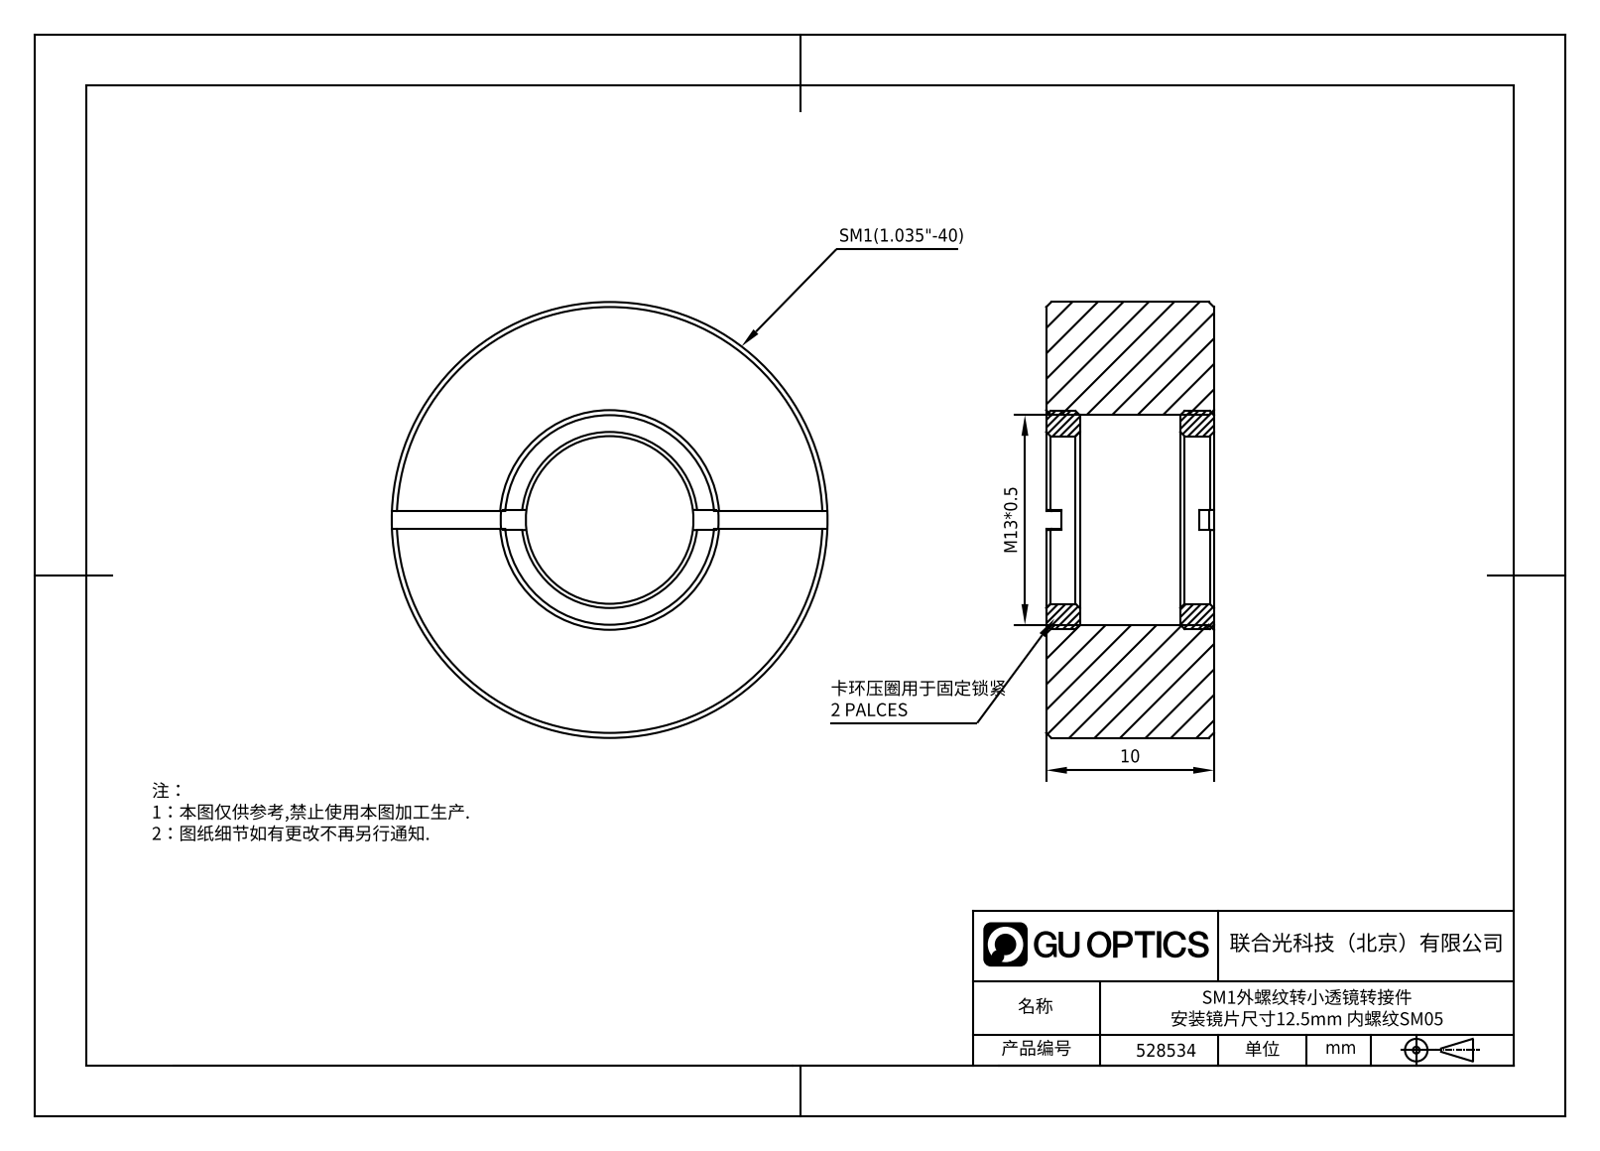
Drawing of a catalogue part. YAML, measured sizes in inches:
part_name: "528534"
step_written_by: "SolidWorks 2020 (CONFIG_CONTROL_DESIGN)"
units: inches
bodies: {solids: 3, faces: 51, planar: 27, cylindrical: 6, other: 18}
overall_size: [1.024, 1.024, 0.394]
volume: 0.26
surface_area: 3.833
round_holes:
  - {diameter: 0.394, count: 1}
  - {diameter: 0.492, count: 1}
round_bosses_or_shafts:
  - {diameter: 1.024, count: 1}
  - {diameter: 0.512, count: 1}
face_to_face_distances: [0.394, 0.079, 0.315, 0.236, 0.039, 0.043, 0.354, 0.276, 0.045, 0.035]
